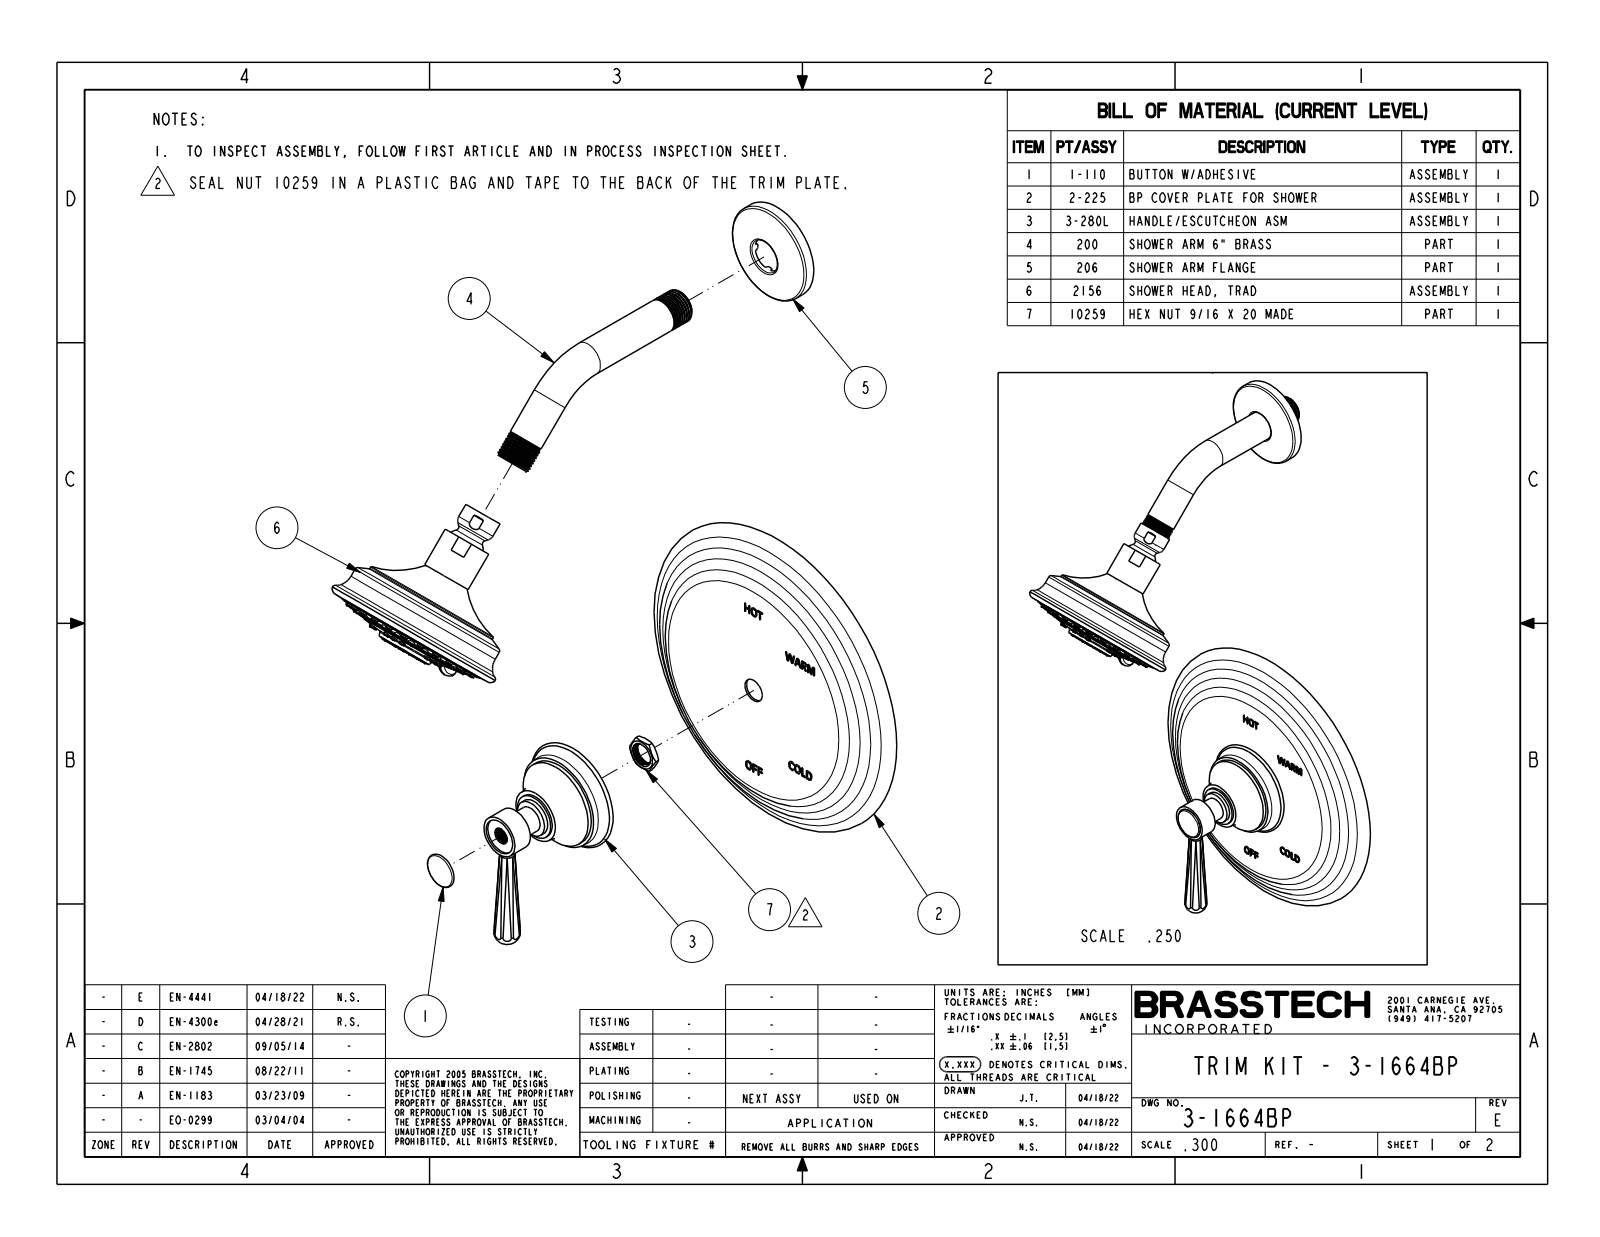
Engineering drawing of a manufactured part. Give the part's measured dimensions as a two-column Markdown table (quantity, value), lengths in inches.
| quantity | value |
| --- | --- |
| part name | 3-1664BP |
| STEP written by | CREO PARAMETRIC BY PTC INC, 2018400 (CONFIG_CONTROL_DESIGN) |
| units | inches |
| bodies | 2 solids, 1324 faces (269 planar, 210 cylindrical, 845 other) |
| overall size | 17.065 × 8.25 × 7.75 |
| volume | 52.41 in³ |
| surface area | 191.2 in² |
| round holes (diameter × count) | 0.059 × 8, 0.363 × 1, 0.85 × 1, 0.925 × 1 |
| round bosses / shafts (diameter × count) | 0.142 × 39, 0.165 × 23, 0.813 × 2, 3.81 × 1, 3.724 × 1, 3.24 × 1, 2.38 × 1, 2.323 × 1 |
| partial cylindrical surfaces (radius × count) | 0.079 × 8, 0.02 × 2, 0.138 × 1, 0.472 × 1, 0.512 × 1, 0.63 × 1 |
| main face-to-face distances | 0.754, 0.063, 0.118, 0.181, 1.229, 0.475, 2.129, 1.375, 0.9, 1.979 |
| hole center spacings | 0.443, 0.579, 0.818, 0.819, 1.069, 0.443, 0.578, 1.069 |
